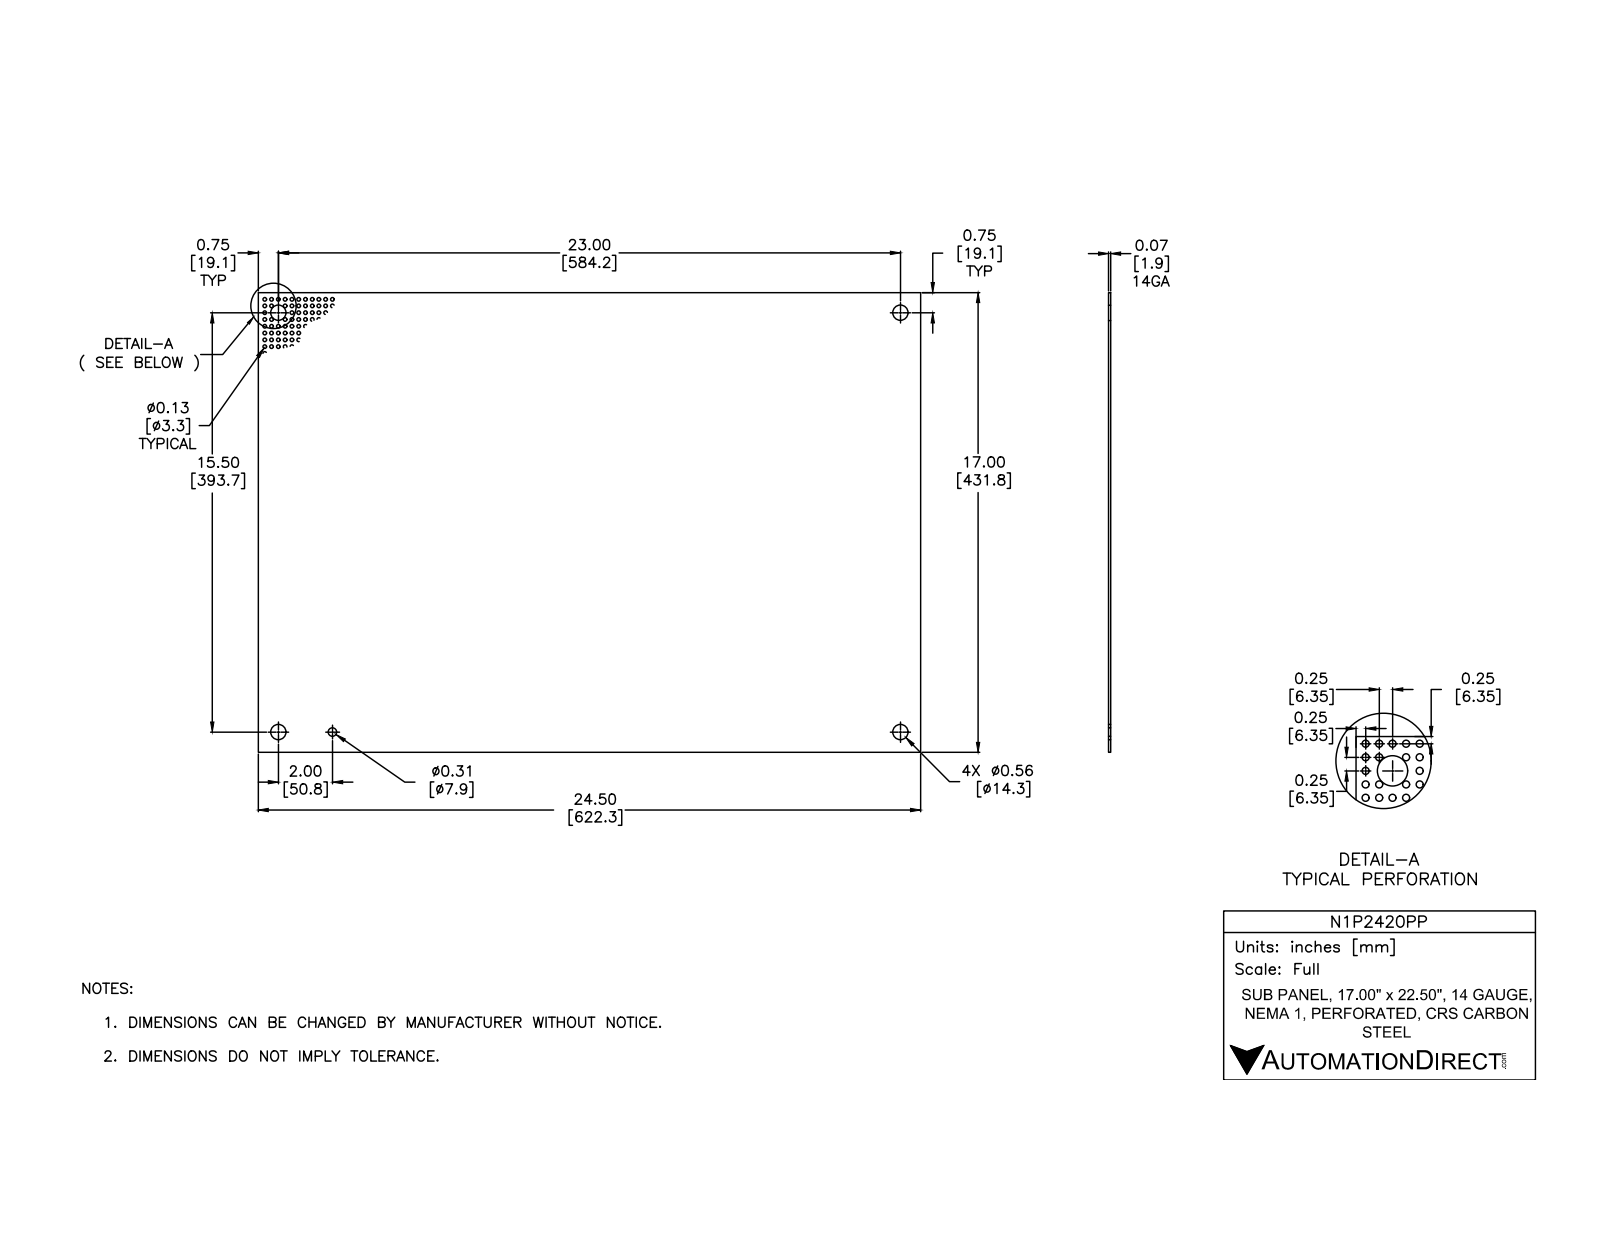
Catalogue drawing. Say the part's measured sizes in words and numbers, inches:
The part is named "N1P_PP-LARGE". Its 3-D file was written by "Autodesk Inventor 2012 (AUTOMOTIVE_DESIGN)". It is 1 solid with 11 faces: 6 planar, 5 cylindrical and 0 other. Overall it measures 22.5 by 17 by 0.074 inches. Its volume is 28.23 cubic inches and its surface area 769.3 square inches. Round holes: 4 of diameter 0.563, 1 of diameter 0.312. The main face-to-face distances are 0.074, 17, 22.5. The hole center spacings are 15.5, 21, 26.101, 2, 15.628, 19, 24.52.
